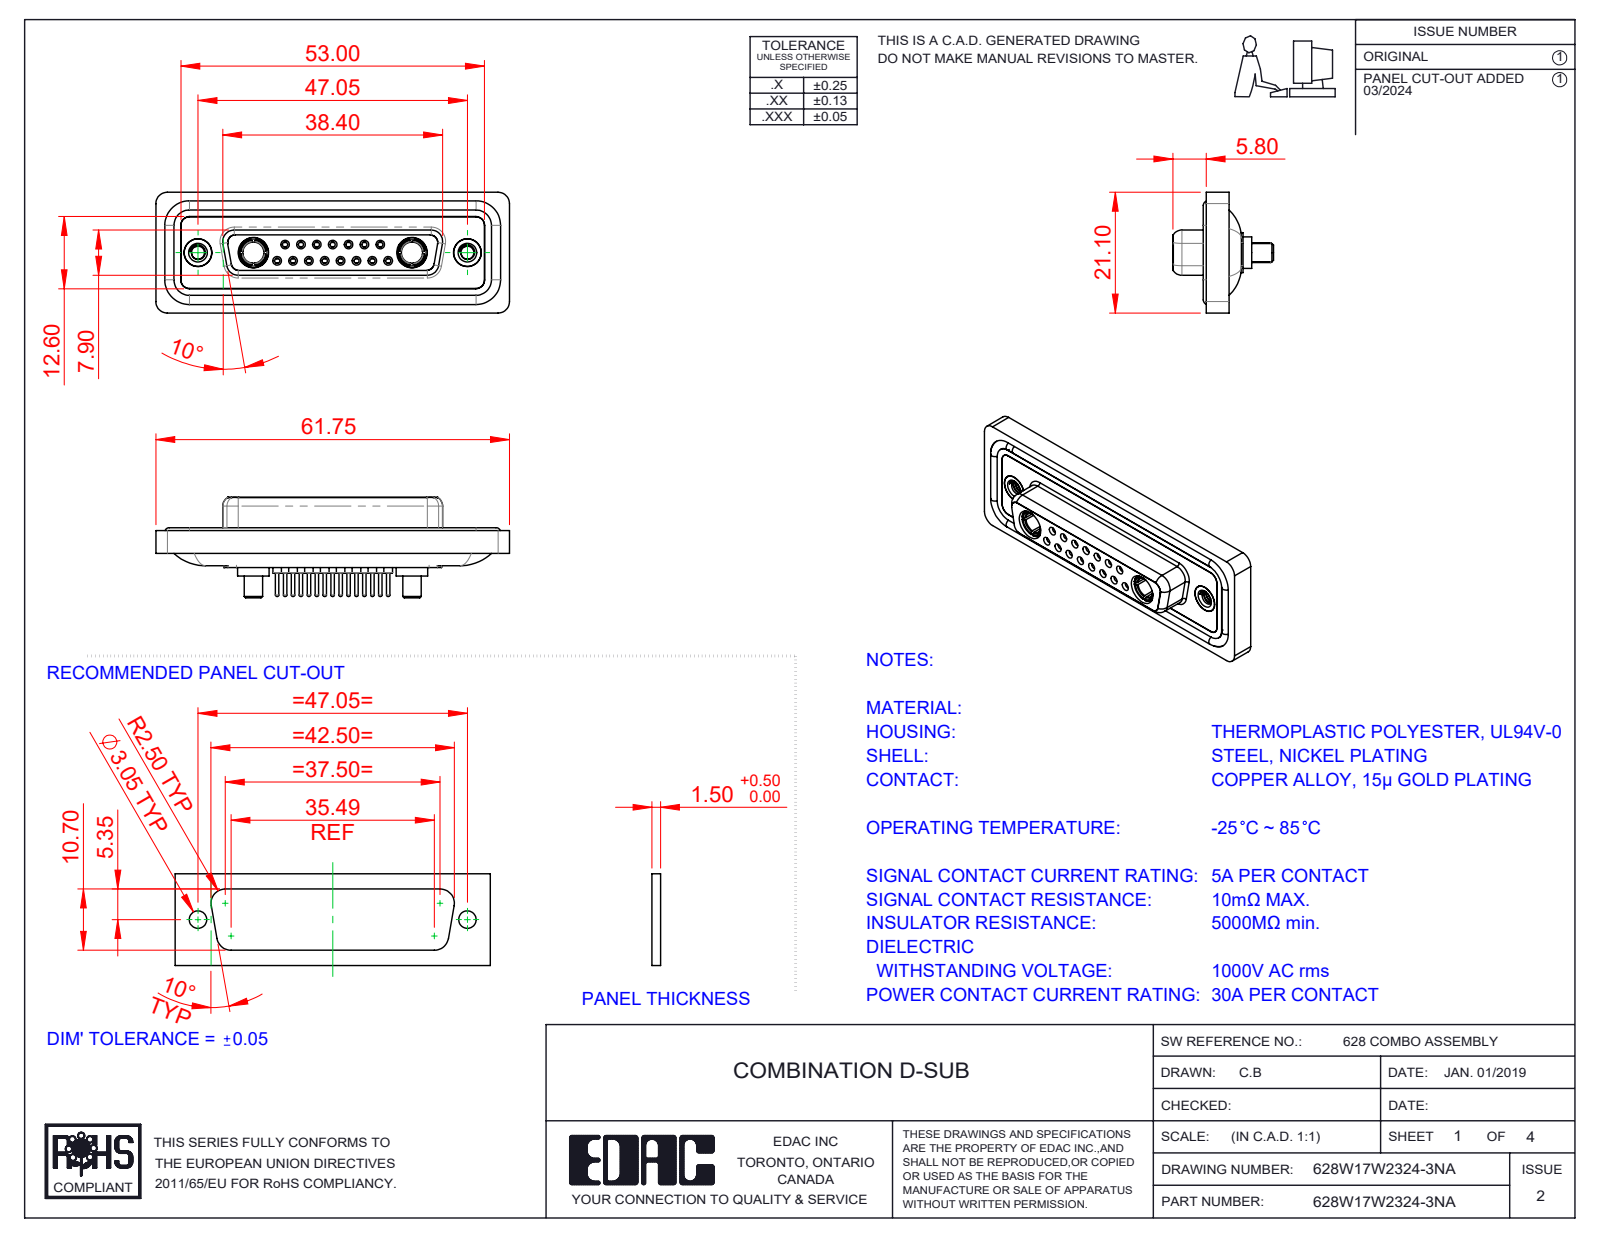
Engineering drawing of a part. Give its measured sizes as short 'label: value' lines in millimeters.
name: 628Combo Waterproof Housing_25 Contacts; 628Combo Threaded Rivet_A; Power Socket_30A S; 628Combo Shell Front_25 Contacts (+5 more)
written by: SolidWorks 2023 (CONFIG_CONTROL_DESIGN)
unit: mm
bodies: 26 solids, 1357 faces (388 planar, 521 cylindrical, 448 other)
size: 61.75 × 21.1 × 17.55
volume: 8 340 mm³; area: 13 862 mm²
holes: 15× ⌀0.9, 15× ⌀1.1, 15× ⌀1.5, 15× ⌀2, 8× ⌀1.6, 7× ⌀1.7, 4× ⌀4.85, 2× ⌀2.26, 2× ⌀3.7, 2× ⌀4, 2× ⌀4.05, 2× ⌀5
bosses: 15× ⌀2.2, 15× ⌀0.6, 11× ⌀1.6, 2× ⌀5.5, 2× ⌀5.2, 2× ⌀4.96, 2× ⌀4.95, 2× ⌀4.8
rounds: 22× R1.5, 18× R2, 8× R1.35, 8× R1.6, 4× R0.25, 4× R0.5, 4× R0.6, 4× R0.65
face distances: 0.4, 1.8, 7.45, 5.65, 6.6, 0.5, 7.05, 1.6, 2.9, 1.1
hole spacings: 3.16, 2.77, 8.31, 5.54, 5.03, 5.04, 7.49, 11.08
